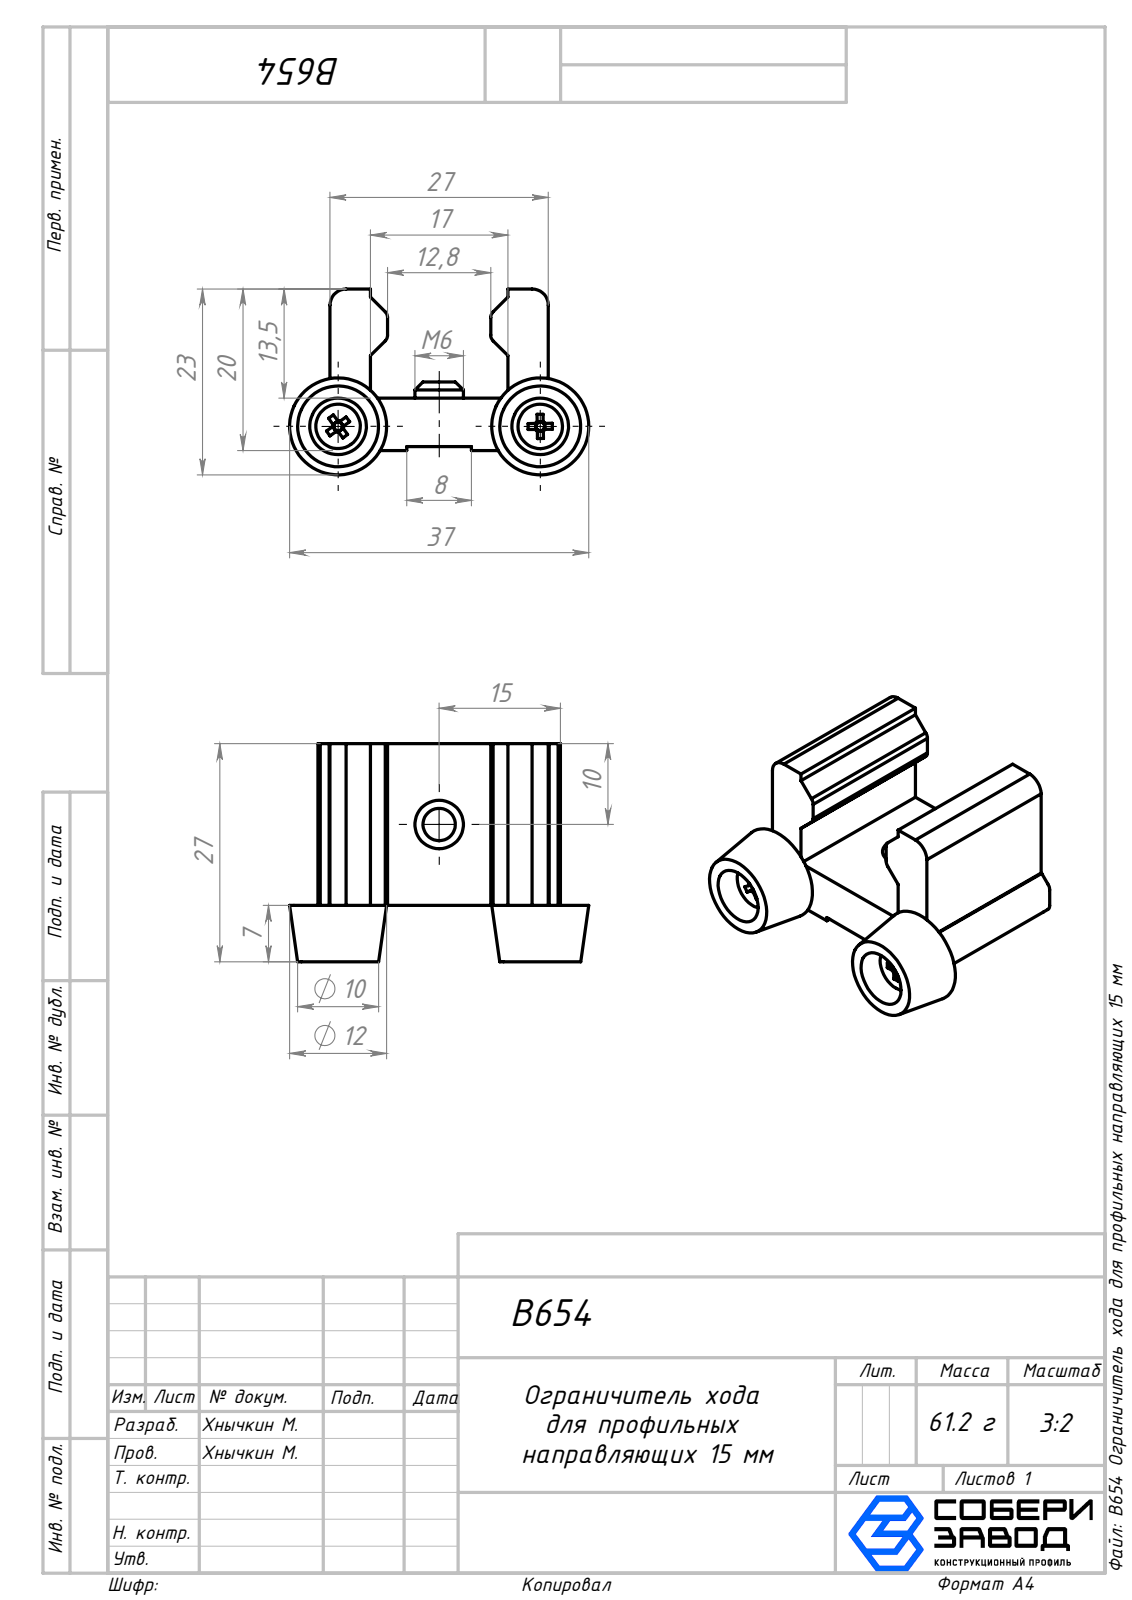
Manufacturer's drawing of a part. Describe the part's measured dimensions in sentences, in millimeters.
The part is named "B654 Ограничитель хода для профильных направляющих 15 мм; countersunk flat head cross recess screw_din_DIN EN ISO 7046-1 - M3 x 6 - Z - 6N; B654 Корпус_00; B654 Конус_00 (+1 more)". Its 3-D file was written by "SolidWorks 2025 (AUTOMOTIVE_DESIGN)". It is 6 solids with 163 faces: 91 planar, 36 cylindrical and 36 other. Overall it measures 37 by 27 by 23 millimeters. Its volume is 7 891 cubic millimeters and its surface area 4 900 square millimeters. Round holes: 2 of diameter 2.5, 2 of diameter 3.5, 2 of diameter 7, 1 of diameter 5. Round bosses or shafts: 2 of diameter 5.5, 2 of diameter 3, 1 of diameter 6. Partial cylindrical surfaces (rounded edges, fillets, slot ends): 10 of radius 1, 2 of radius 2. The main face-to-face distances are 20, 6.5, 27, 5, 22, 6, 0.5, 17, 19.5, 13.5. The hole center spacings are 25.
